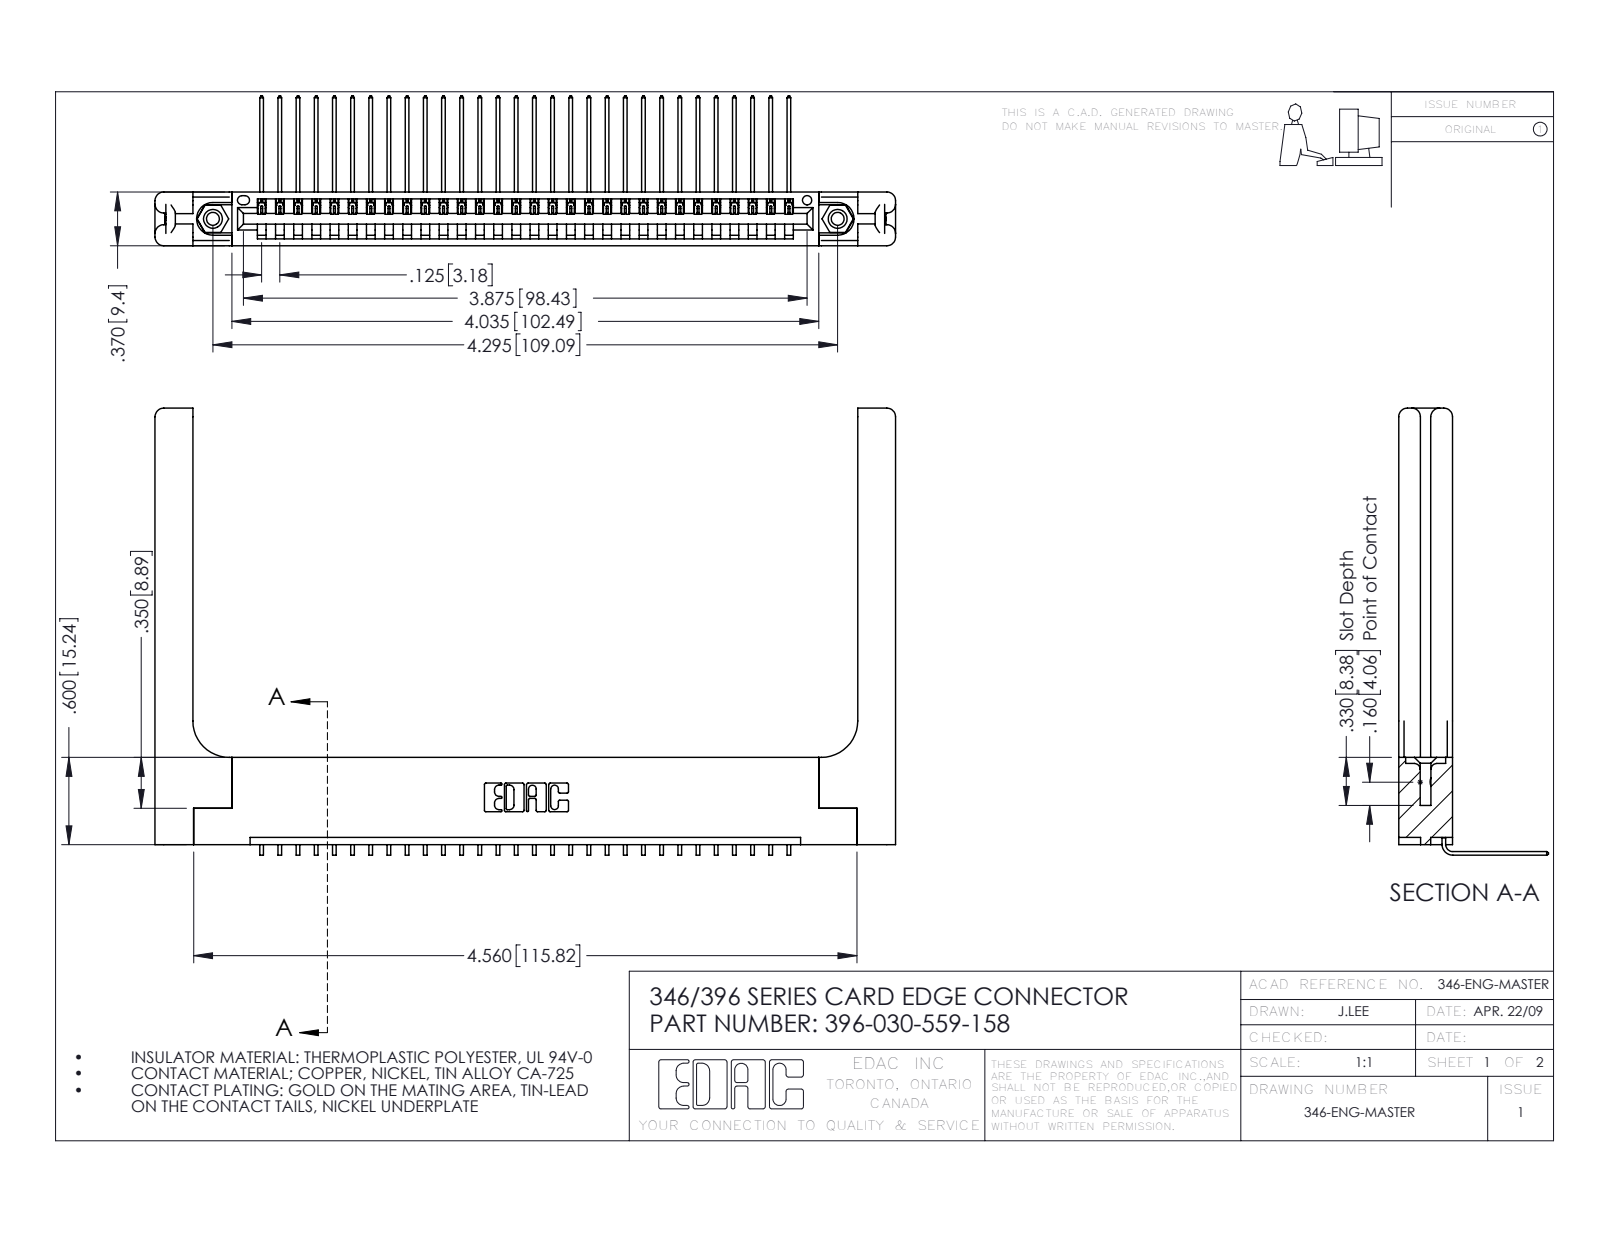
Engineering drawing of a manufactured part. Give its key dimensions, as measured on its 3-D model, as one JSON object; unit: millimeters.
{"part_name": "346-220-058_345-220-058; 396-030-559-158; 345-292-001_558 559 Tail - 1; 346 Part_Flush Mounting Lugs - 0.156 Dia-TH (+1 more)", "step_written_by": "SolidWorks 2016 (CONFIG_CONTROL_DESIGN)", "units": "millimeters", "bodies": {"solids": 35, "faces": 2178, "planar": 1484, "cylindrical": 634, "other": 60}, "overall_size": [129.3, 78.1, 26.2], "volume_mm3": 19910, "surface_area_mm2": 21130, "round_holes": [[2.3, 2], [3.2, 2], [4, 2], [1.6, 1]], "round_bosses_or_shafts": [[3.9, 2]], "partial_cylinders_radius": [[0.2, 60], [0.3, 22], [1.5, 16], [0.2, 6], [0.8, 6], [0.7, 3], [0.8, 2], [0.8, 2]], "face_to_face_distances": [9.4, 1.8, 1.2, 8.2, 3.8, 3.8, 0.6, 6.4, 7.6, 1.9], "hole_center_spacings": [6.2, 103.8, 109.1]}
